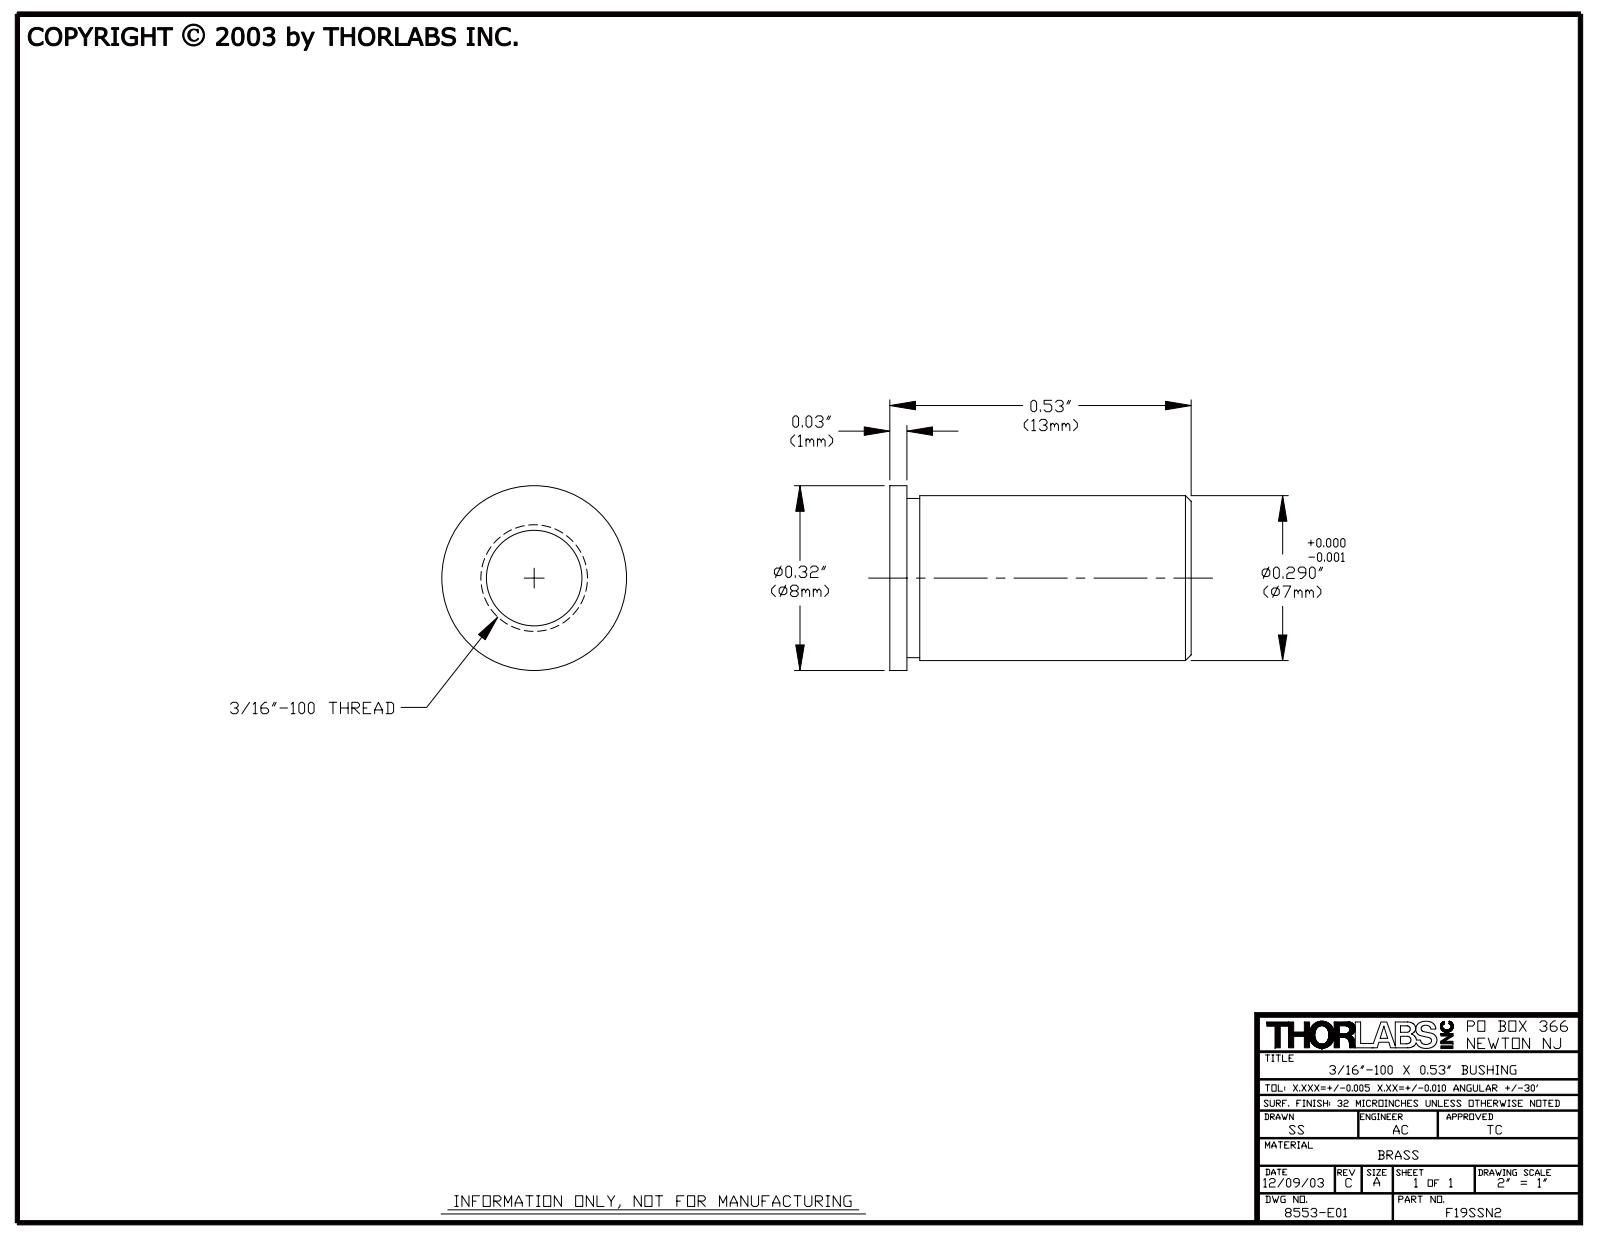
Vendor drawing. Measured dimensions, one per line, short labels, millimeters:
name: 8553-E0W
written by: SolidWorks 2007 (AUTOMOTIVE_DESIGN)
unit: mm
bodies: 1 solid, 226 faces (3 planar, 219 cylindrical, 4 other)
size: 13.5 × 8.3 × 8.3
volume: 360 mm³; area: 860 mm²
holes: 1× ⌀4.3, 1× ⌀4.7
bosses: 1× ⌀8.3, 1× ⌀7.4
face distances: 13.5, 12.7, 0.8
